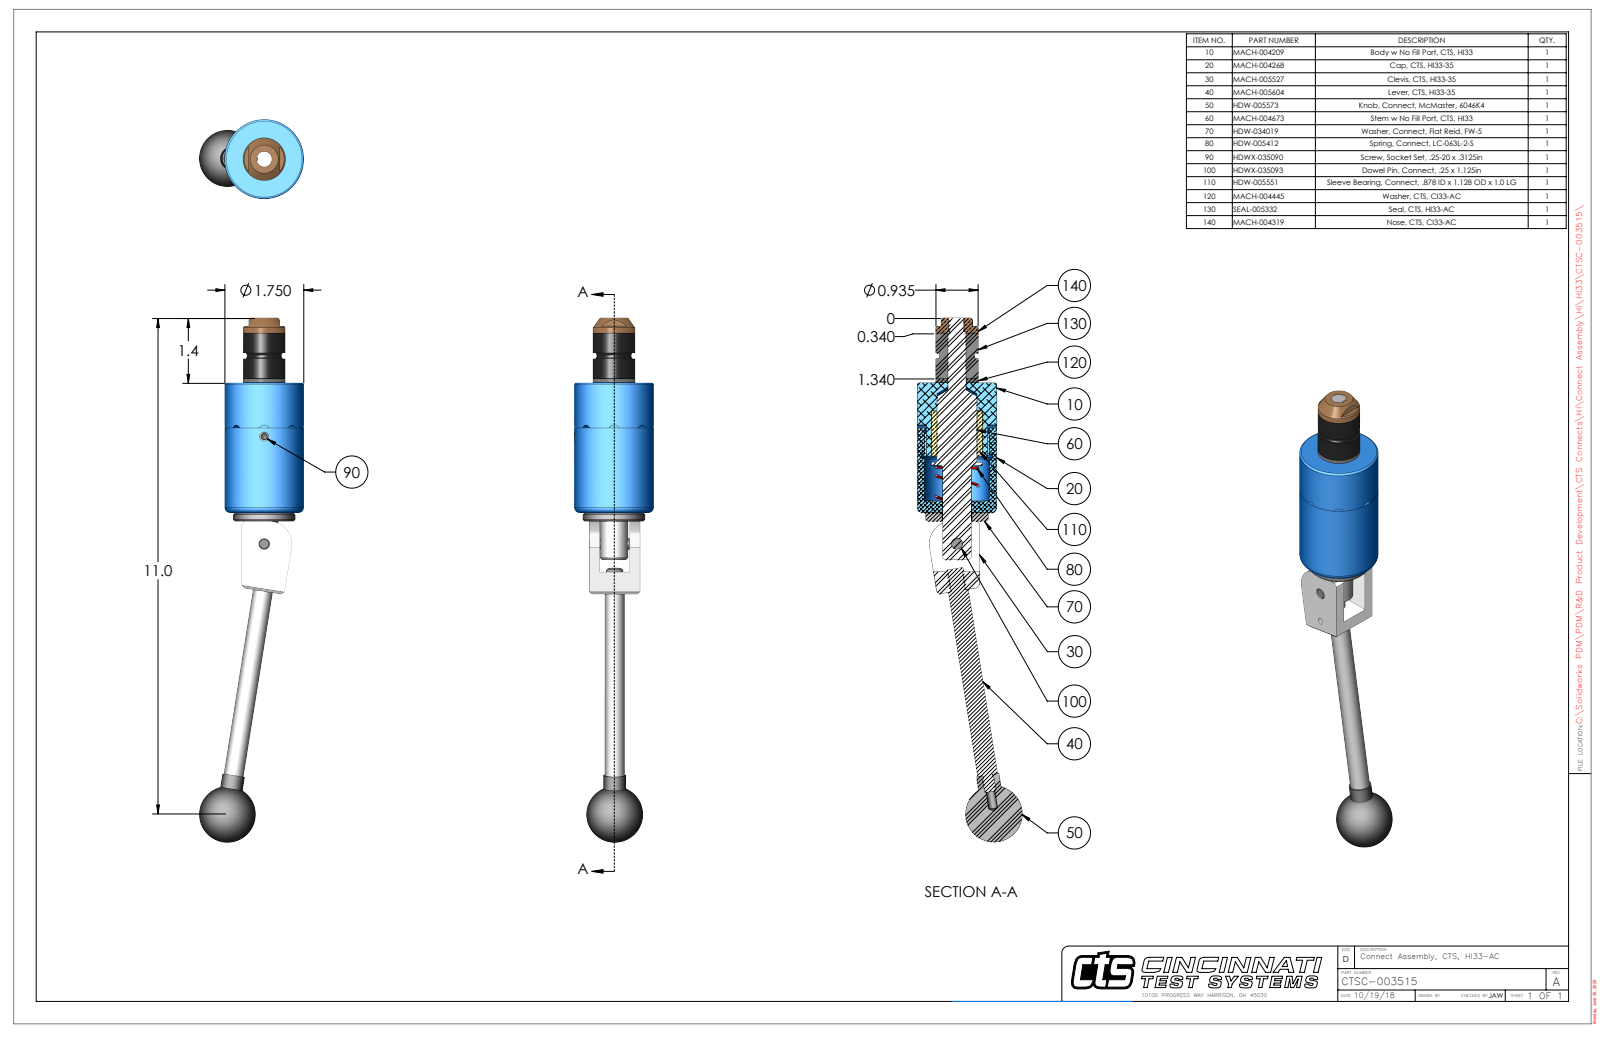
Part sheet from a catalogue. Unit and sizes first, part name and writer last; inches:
Units: inches
Overall size (bounding box): 11.613 × 2.312 × 1.75
Round holes (diameter × count): ⌀0.201 ×2, ⌀0.313 ×2, ⌀0.15 ×1, ⌀0.249 ×1, ⌀0.251 ×1, ⌀0.39 ×1, ⌀0.397 ×1, ⌀0.403 ×1, ⌀0.635 ×1, ⌀0.656 ×1, ⌀1.419 ×1
Round bosses / shafts (diameter × count): ⌀0.375 ×2, ⌀0.312 ×2, ⌀0.25 ×2, ⌀1.75 ×1, ⌀1.38 ×1, ⌀0.935 ×1, ⌀0.625 ×1, ⌀0.5 ×1
Partial cylindrical surfaces — rounded edges, fillets, slot ends (radius × count): R0.125 ×4, R0.029 ×2, R0.5 ×1, R0.695 ×1, R0.825 ×1
Main face-to-face distances: 2.878, 1.098, 1.12, 1, 3.066, 0.188, 3.976, 4.164, 0.888, 0.232
Hole centre spacings: 0.74, 2.376, 3.116
Volume: 11.04 in³ · Surface area: 62.34 in²
Bodies: 9 solids, 233 faces (78 planar, 96 cylindrical, 59 other)
Part name (STEP PRODUCT): CTSC-003515
STEP written by: SolidWorks 2023 (AUTOMOTIVE_DESIGN)
